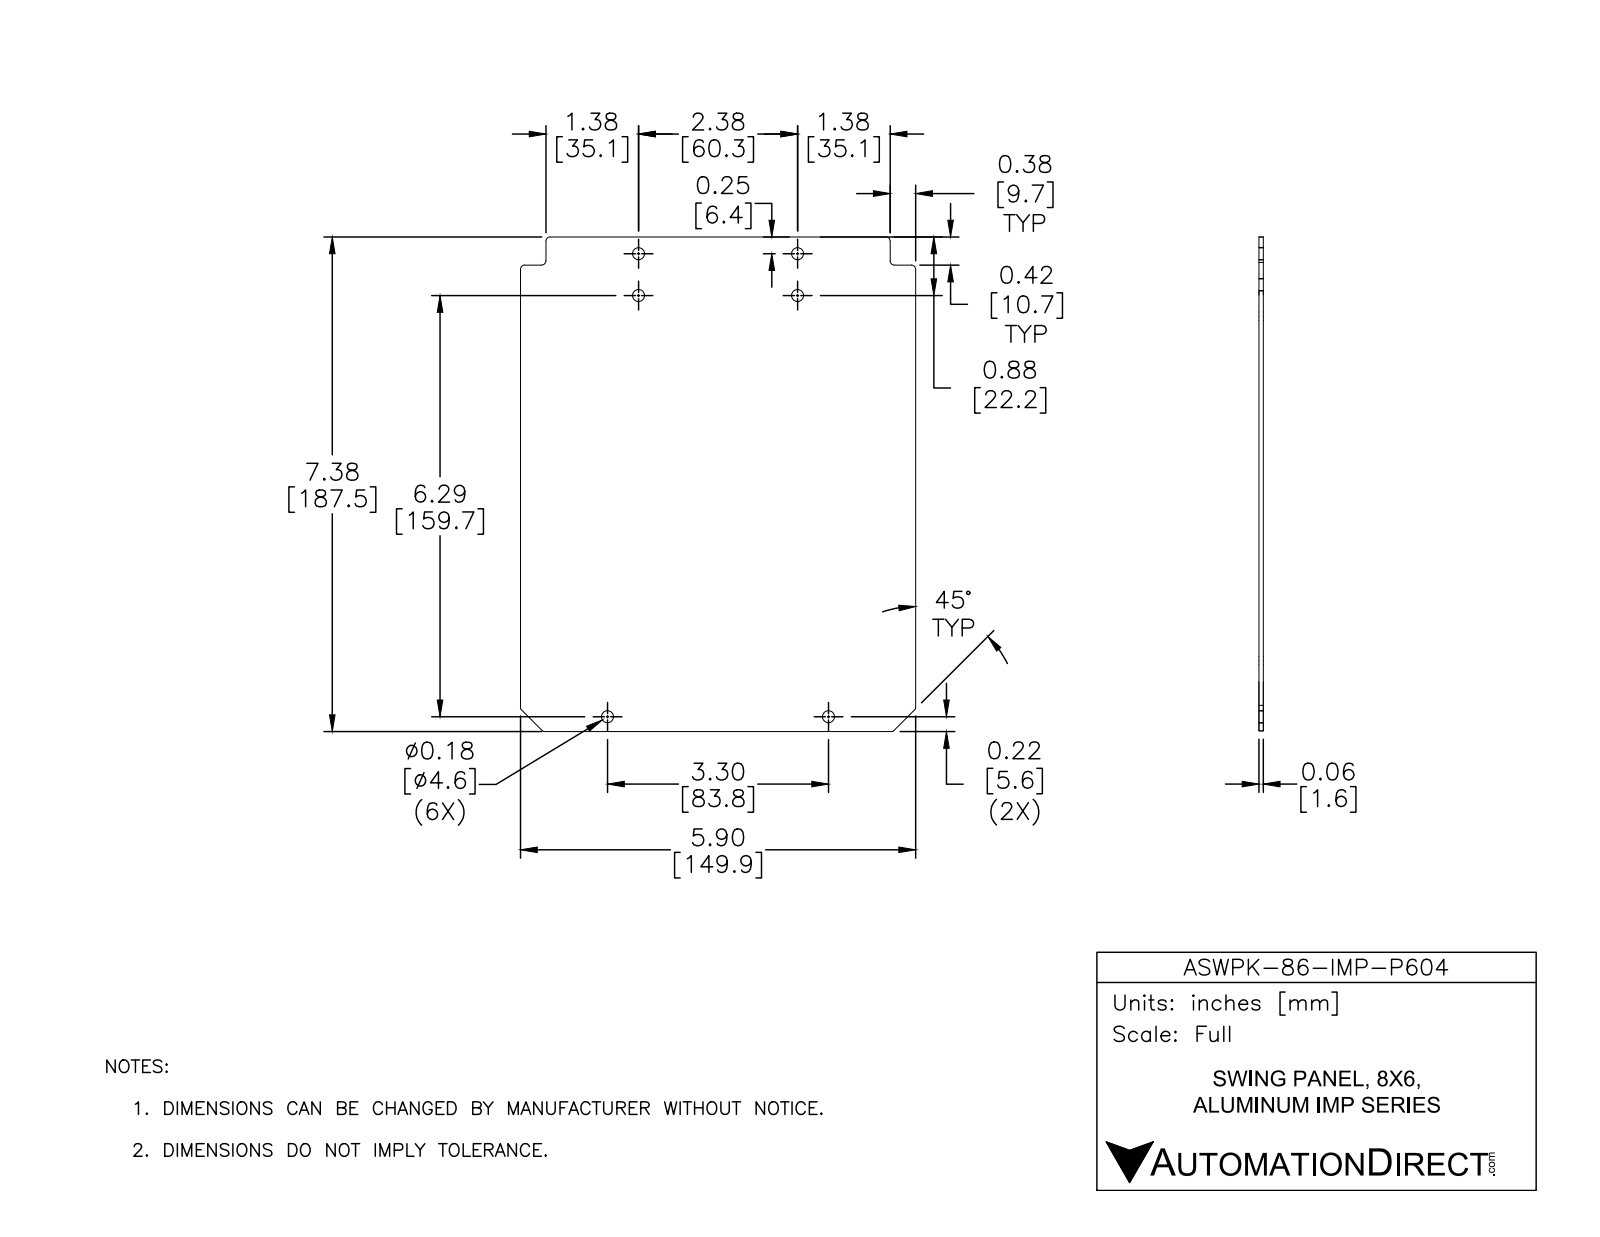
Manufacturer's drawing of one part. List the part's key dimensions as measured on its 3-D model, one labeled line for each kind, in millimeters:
Part name (STEP PRODUCT): ASWPK-86-IMP-P604
STEP written by: SolidWorks 2016 (AUTOMOTIVE_DESIGN)
Units: millimetres
Bodies: 1 solid, 34 faces (12 planar, 22 cylindrical, 0 other)
Overall size (bounding box): 187.5 × 149.9 × 1.6
Volume: 45 130 mm³ · Surface area: 56 660 mm²
Round holes (diameter × count): ⌀4.6 ×6
Partial cylindrical surfaces — rounded edges, fillets, slot ends (radius × count): R1.6 ×6, R1 ×2, R1 ×1, R1 ×1
Main face-to-face distances: 1.6, 149.9, 187.5, 176.9, 10.7, 140.2, 9.7, 9.7, 130.6, 140.2
Hole centre spacings: 15.9, 60.3, 62.4, 160.1, 175.2, 176, 189.8, 83.8
